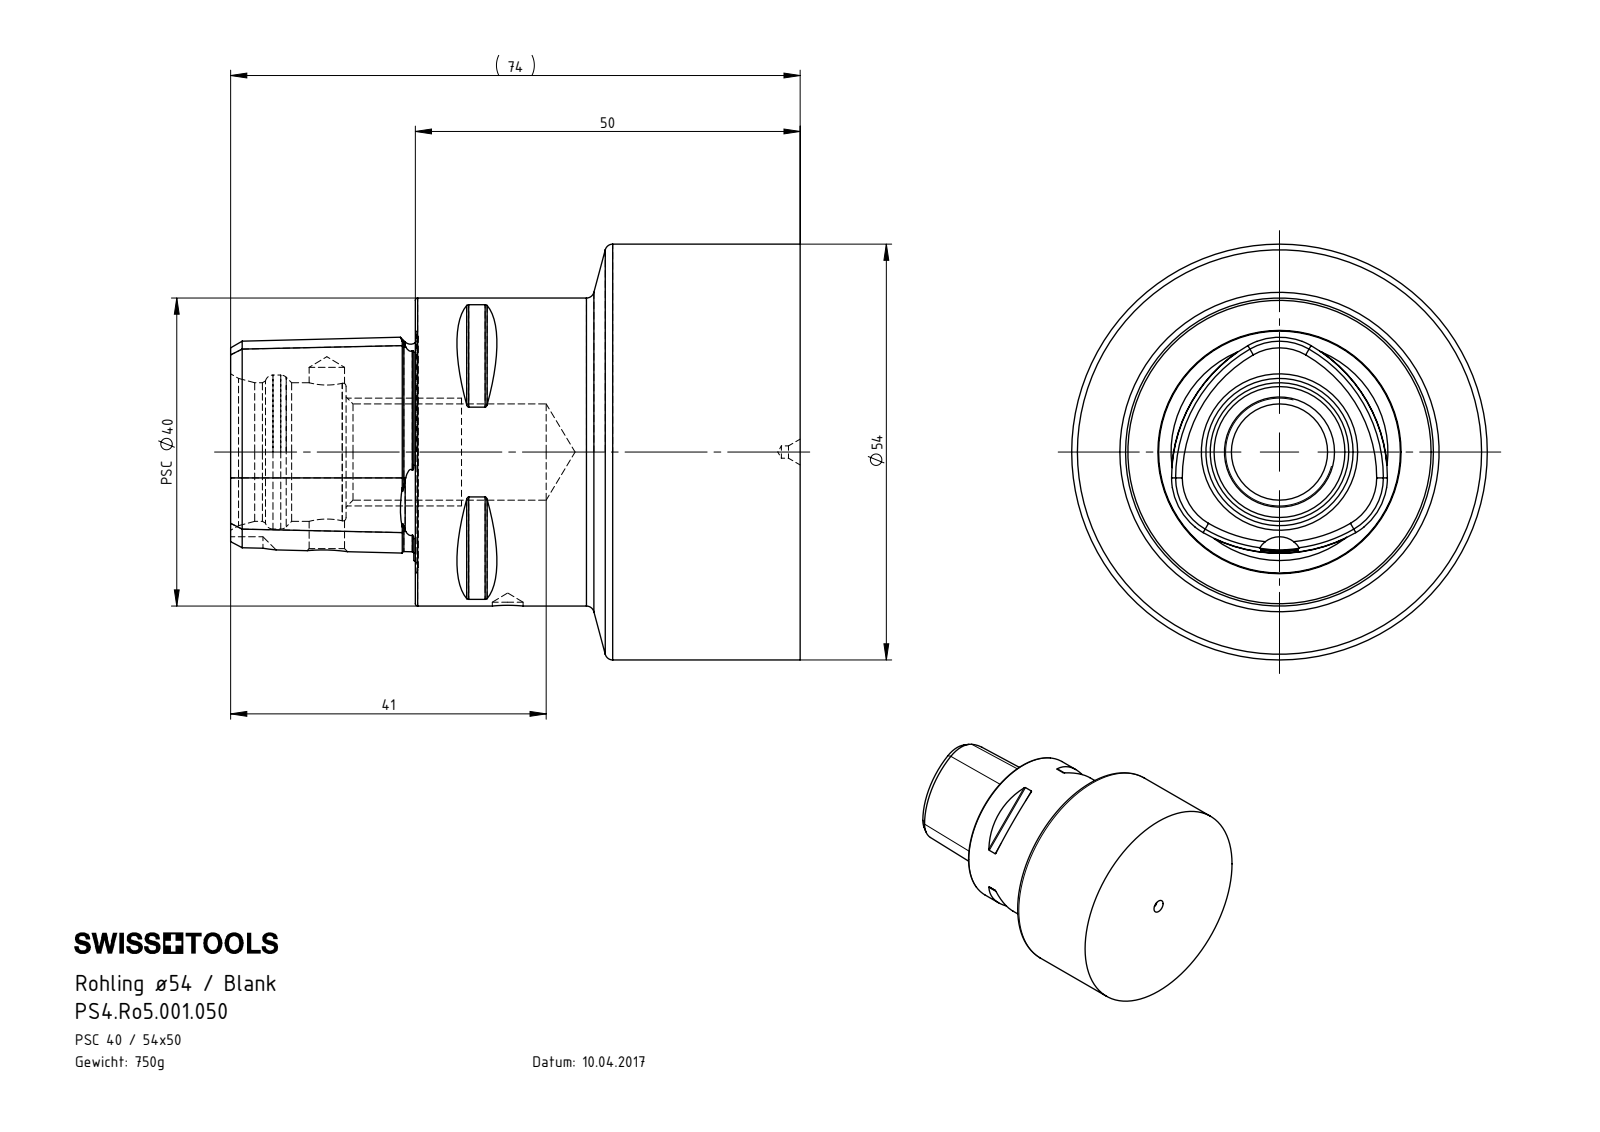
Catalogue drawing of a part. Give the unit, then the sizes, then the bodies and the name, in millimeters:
Units: millimetres
Overall size (bounding box): 74 × 54 × 54
Round holes (diameter × count): ⌀1.6 ×1, ⌀4 ×1, ⌀4.6 ×1, ⌀12.5 ×1, ⌀18 ×1, ⌀20 ×1
Round bosses / shafts (diameter × count): ⌀54 ×1, ⌀40 ×1
Partial cylindrical surfaces — rounded edges, fillets, slot ends (radius × count): R0.3 ×8, R3 ×1
Main face-to-face distances: 50, 24, 74, 15.52, 35.3, 15, 9, 59, 23.8, 8.8
Hole centre spacings: 23.5
Volume: 95 600 mm³ · Surface area: 15 786 mm²
Bodies: 1 solid, 96 faces (19 planar, 19 cylindrical, 58 other)
Part name (STEP PRODUCT): PS4.Ro5.001.050
STEP written by: SolidWorks 2017 (AUTOMOTIVE_DESIGN)
